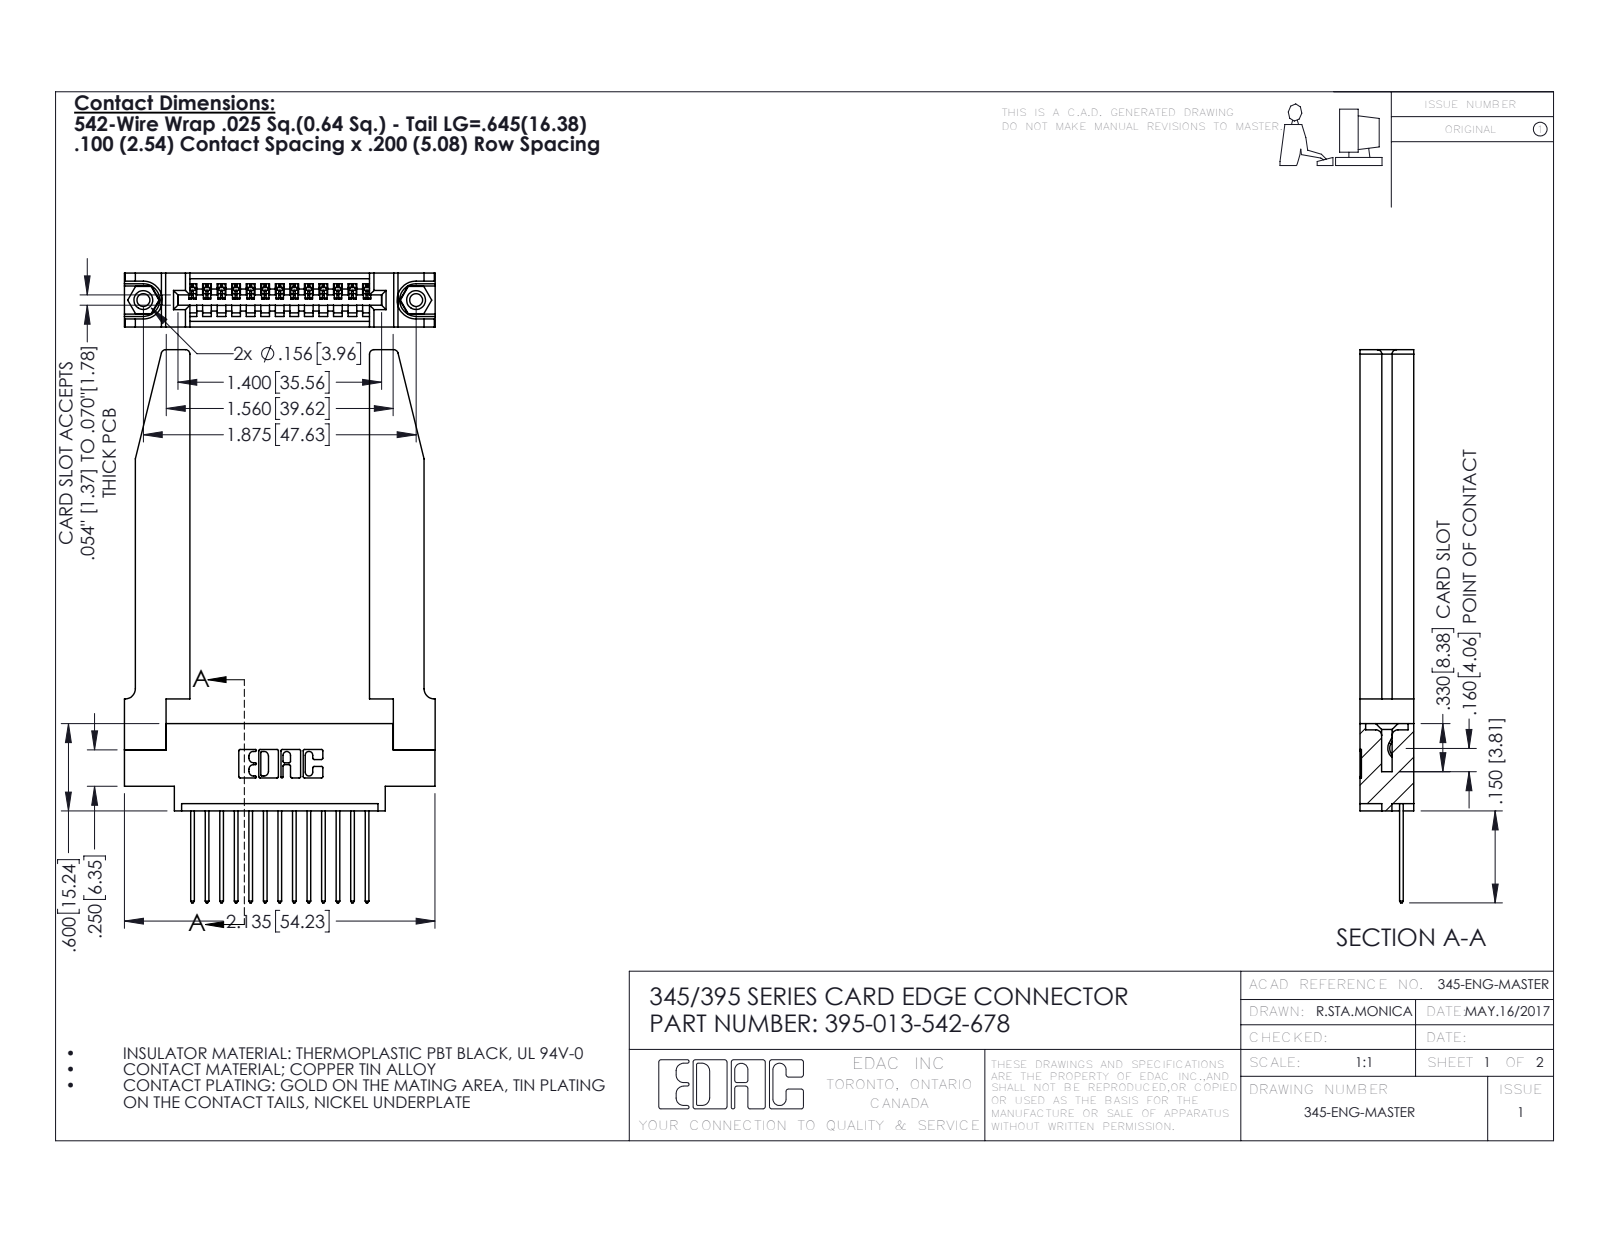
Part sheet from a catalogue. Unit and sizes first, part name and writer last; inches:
Units: inches
Overall size (bounding box): 3.802 × 2.136 × 0.37
Round holes (diameter × count): ⌀0.089 ×2, ⌀0.125 ×2, ⌀0.156 ×2, ⌀0.064 ×1
Round bosses / shafts (diameter × count): ⌀0.155 ×2
Partial cylindrical surfaces — rounded edges, fillets, slot ends (radius × count): R0.006 ×26, R0.01 ×26, R0.01 ×22, R0.03 ×8, R0.007 ×6, R0.031 ×6, R0.026 ×3, R0.031 ×2
Main face-to-face distances: 0.37, 0.072, 0.298, 0.148, 0.15, 0.22, 0.077, 0.098, 0.272, 0.025
Hole centre spacings: 0.27, 1.643, 1.875
Volume: 0.769 in³ · Surface area: 20.43 in²
Bodies: 18 solids, 1118 faces (746 planar, 320 cylindrical, 52 other)
Part name (STEP PRODUCT): 345 Part_0.170 Offset - 0.156 Dia-TH; 345-292-001_345-293-142; 345-250-001_345-250-001-102; 345-220-078_345-220-078 (+1 more)
STEP written by: SolidWorks 2016 (CONFIG_CONTROL_DESIGN)
